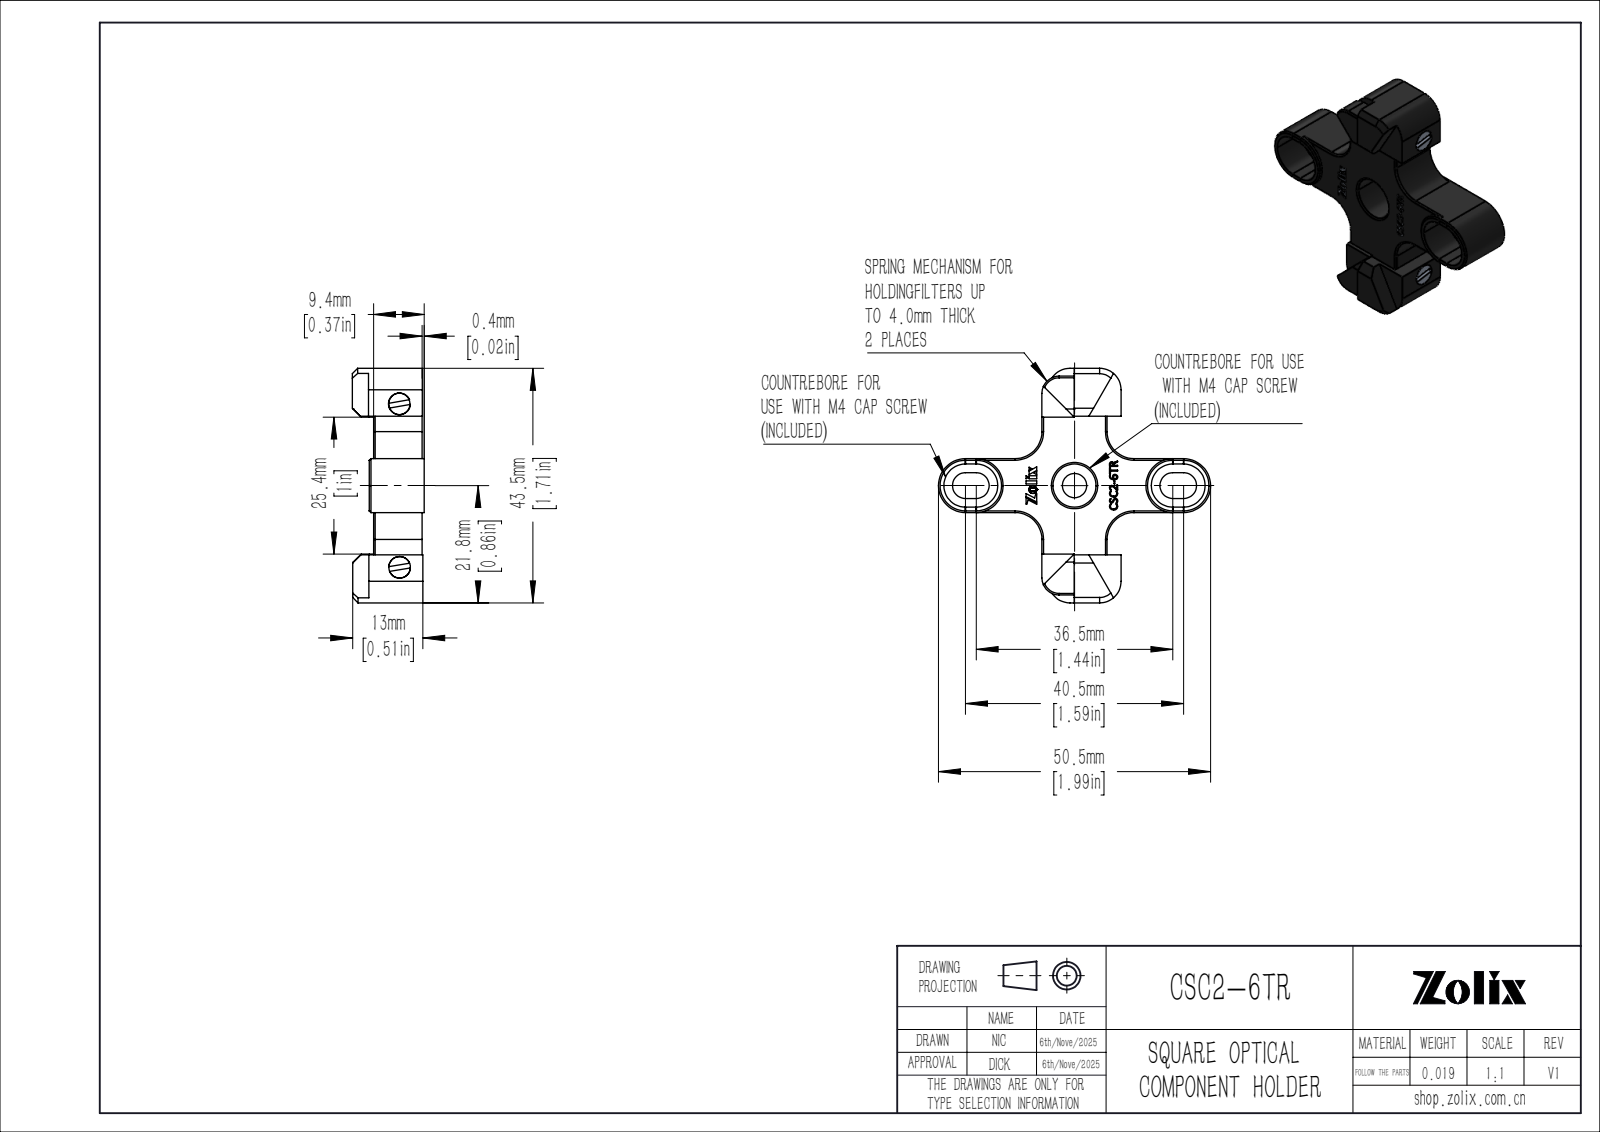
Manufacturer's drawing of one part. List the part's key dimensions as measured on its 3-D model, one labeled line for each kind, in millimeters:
Part name (STEP PRODUCT): CSC2-6TR
STEP written by: SolidWorks 2020 (CONFIG_CONTROL_DESIGN)
Units: millimetres
Bodies: 7 solids, 572 faces (362 planar, 96 cylindrical, 114 other)
Overall size (bounding box): 50.5 × 43.52 × 13.35
Volume: 7 152 mm³ · Surface area: 5 970 mm²
Round holes (diameter × count): ⌀2.2 ×3, ⌀3.4 ×3, ⌀1.6 ×2, ⌀4 ×2, ⌀4.5 ×1, ⌀8 ×1
Round bosses / shafts (diameter × count): ⌀2.18 ×2, ⌀2 ×2, ⌀1.3 ×2, ⌀4 ×1
Partial cylindrical surfaces — rounded edges, fillets, slot ends (radius × count): R0.3 ×8, R4 ×8, R5 ×8, R3.2 ×6, R2.4 ×4, R3 ×4, R1.4 ×2, R2 ×2
Main face-to-face distances: 9.4, 8.9, 9, 0.4, 10, 10.1, 16.76, 4.6, 0.5, 5.5
Hole centre spacings: 30.32
